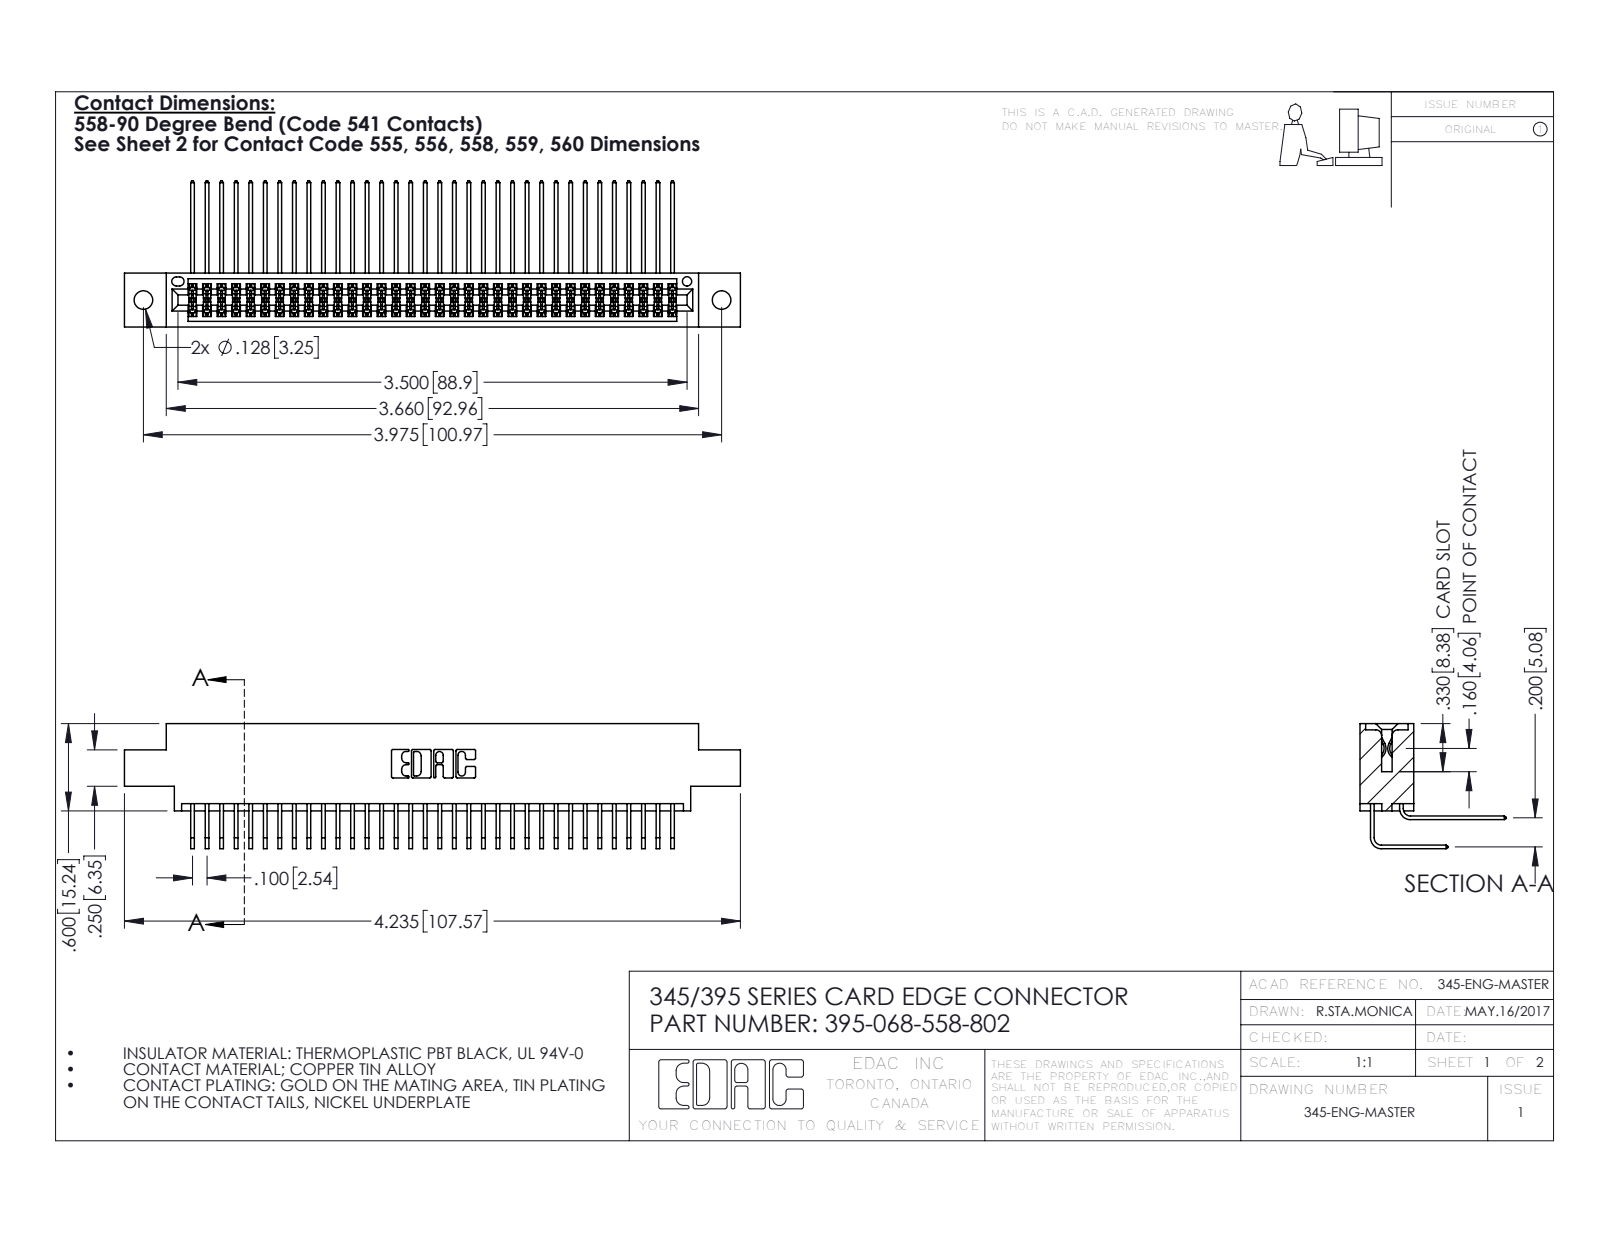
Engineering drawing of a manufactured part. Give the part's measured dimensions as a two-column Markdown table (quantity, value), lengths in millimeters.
| quantity | value |
| --- | --- |
| part name | 345-292-001_558 Tail - 2; 395-068-558-802; 345 Part_0.170 Offset - 0.128 Dia; 345-292-001_558 559 Tail - 1 |
| STEP written by | SolidWorks 2016 (CONFIG_CONTROL_DESIGN) |
| units | millimeters |
| bodies | 69 solids, 3666 faces (2464 planar, 1202 cylindrical, 0 other) |
| overall size | 107.6 × 25.5 × 21.8 |
| volume | 10 600 mm³ |
| surface area | 17 250 mm² |
| round holes (diameter × count) | 3.3 × 2, 1.6 × 1 |
| partial cylindrical surfaces (radius × count) | 0.2 × 103, 0.3 × 22, 0.2 × 6, 0.8 × 6, 0.7 × 3, 0.4 × 2, 0.5 × 2, 0.6 × 2 |
| main face-to-face distances | 1.8, 7.6, 5.1, 9.4, 2.5, 6.9, 0.6, 5.7, 4.4, 0.6 |
| hole center spacings | 6.9, 95, 101 |
